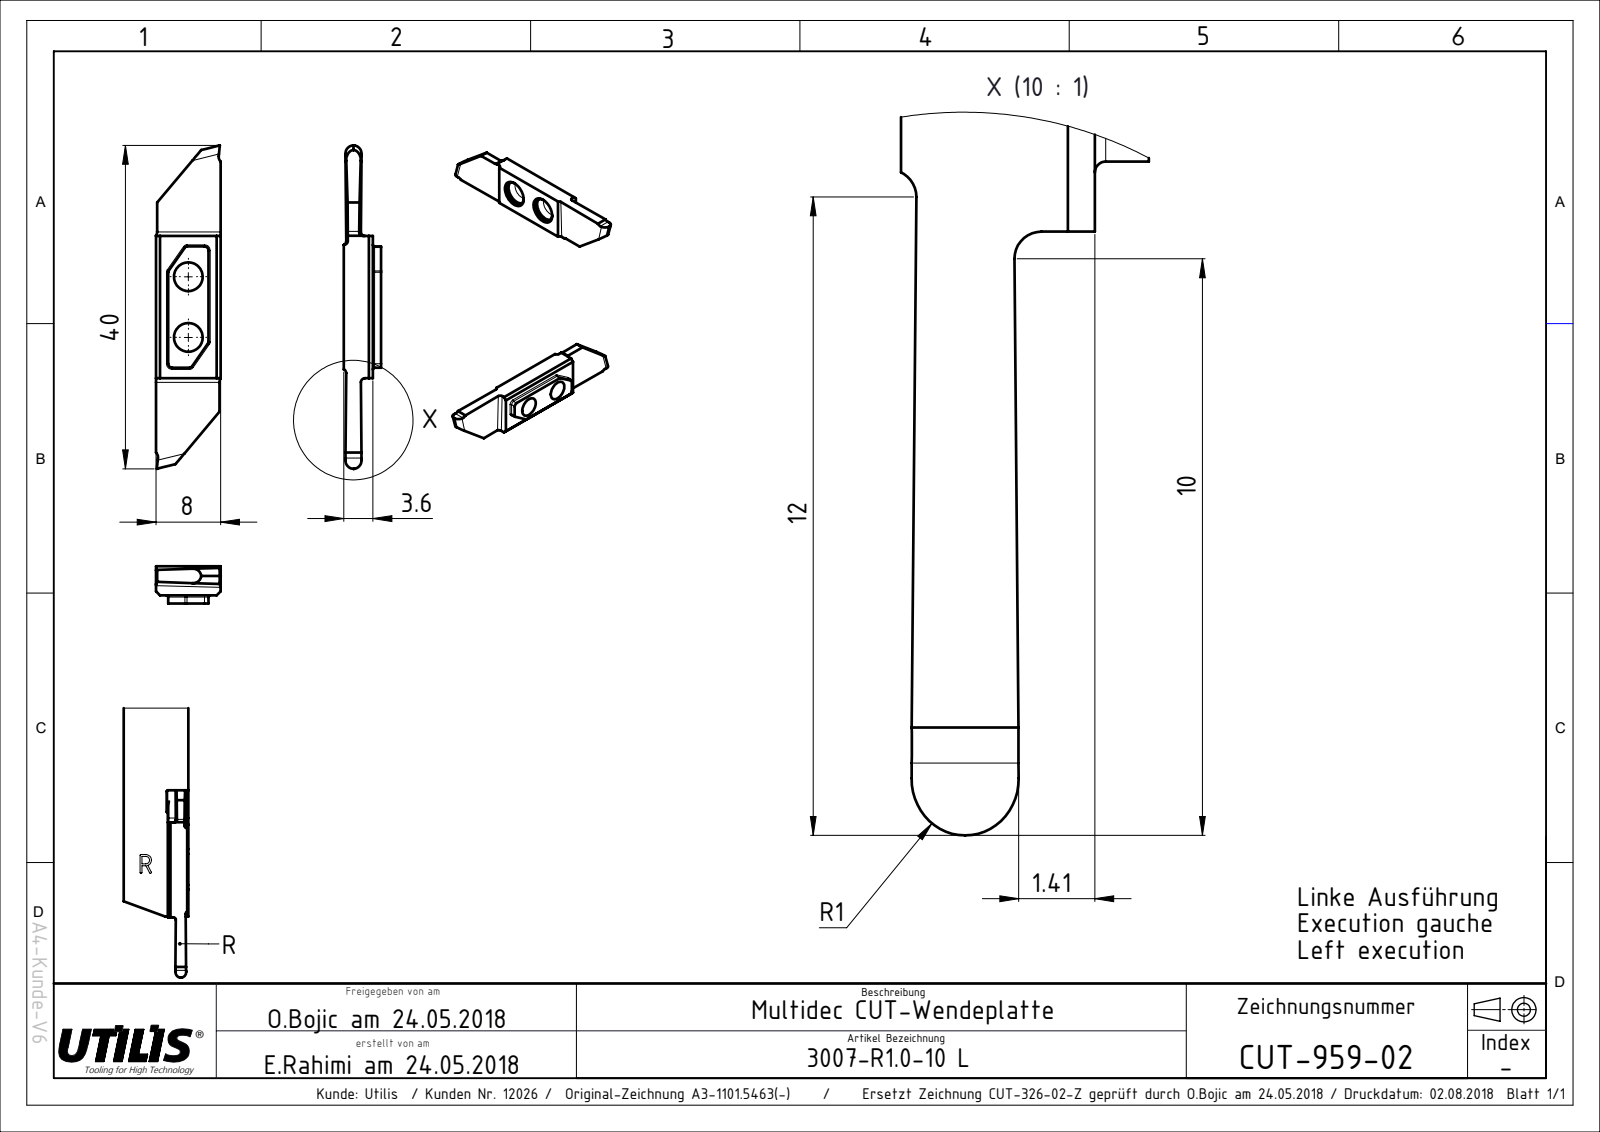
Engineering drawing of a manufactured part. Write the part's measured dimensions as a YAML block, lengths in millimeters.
part_name: "CUT-959; ASME Y14.5"
step_written_by: "FormatWorks Professional (AP242_MANAGED_MODEL_BASED_3D_ENGINEERING_MIM_LF)"
units: millimeters
bodies: {solids: 1, faces: 36, planar: 18, cylindrical: 16, other: 2}
overall_size: [40, 8, 3.6]
volume: 655
surface_area: 818
round_holes:
  - {diameter: 3.55, count: 2}
partial_cylinders:
  - {radius: 1, count: 6}
  - {radius: 0.5, count: 2}
  - {radius: 0.8, count: 2}
face_to_face_distances: [3.6, 8, 1.46, 1.45, 22.54, 7.85, 17.6, 7.7, 7.18]
hole_center_spacings: [7.5]
